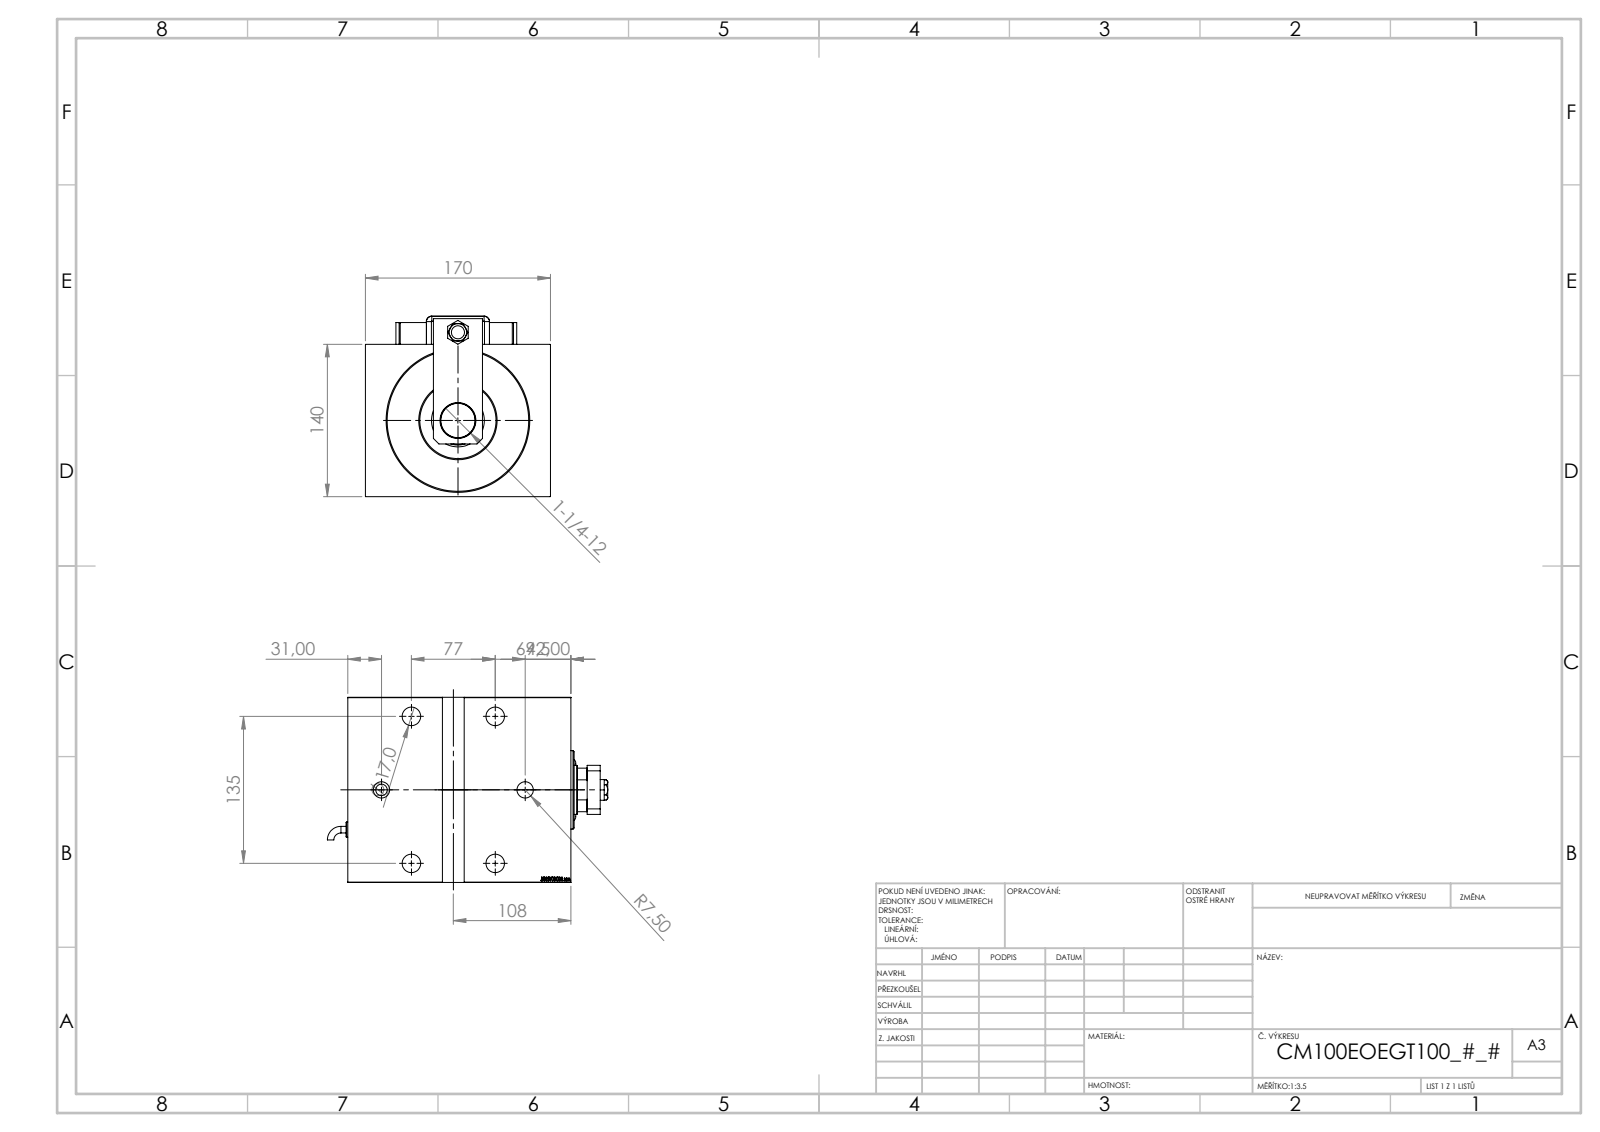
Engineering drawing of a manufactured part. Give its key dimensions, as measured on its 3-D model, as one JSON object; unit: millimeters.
{"part_name": "MAGNETIC SWITCH Q; V450CM_E_Body; V450CM_VC_B; TYC (+8 more)", "step_written_by": "SolidWorks 2019 (CONFIG_CONTROL_DESIGN)", "units": "millimeters", "bodies": {"solids": 13, "faces": 1233, "planar": 615, "cylindrical": 101, "other": 517}, "overall_size": [257.66, 170, 165.8], "volume_mm3": 4311000, "surface_area_mm2": 442836, "round_holes": [[17, 4], [25, 4], [4, 2], [8, 2], [15, 2], [12, 1], [13, 1], [14, 1], [31.5, 1], [33, 1], [45, 1], [48.5, 1]], "round_bosses_or_shafts": [[20, 3], [16, 2], [14, 2], [6, 2], [102, 1], [72, 1], [10.5, 1]], "partial_cylinders_radius": [[5, 9], [10, 1], [22, 1]], "face_to_face_distances": [140, 170, 205, 3, 26, 179, 5, 200, 174, 165.8], "hole_center_spacings": [72.89, 124.4, 37.36, 77, 85.67, 100.19, 135, 151.81]}
